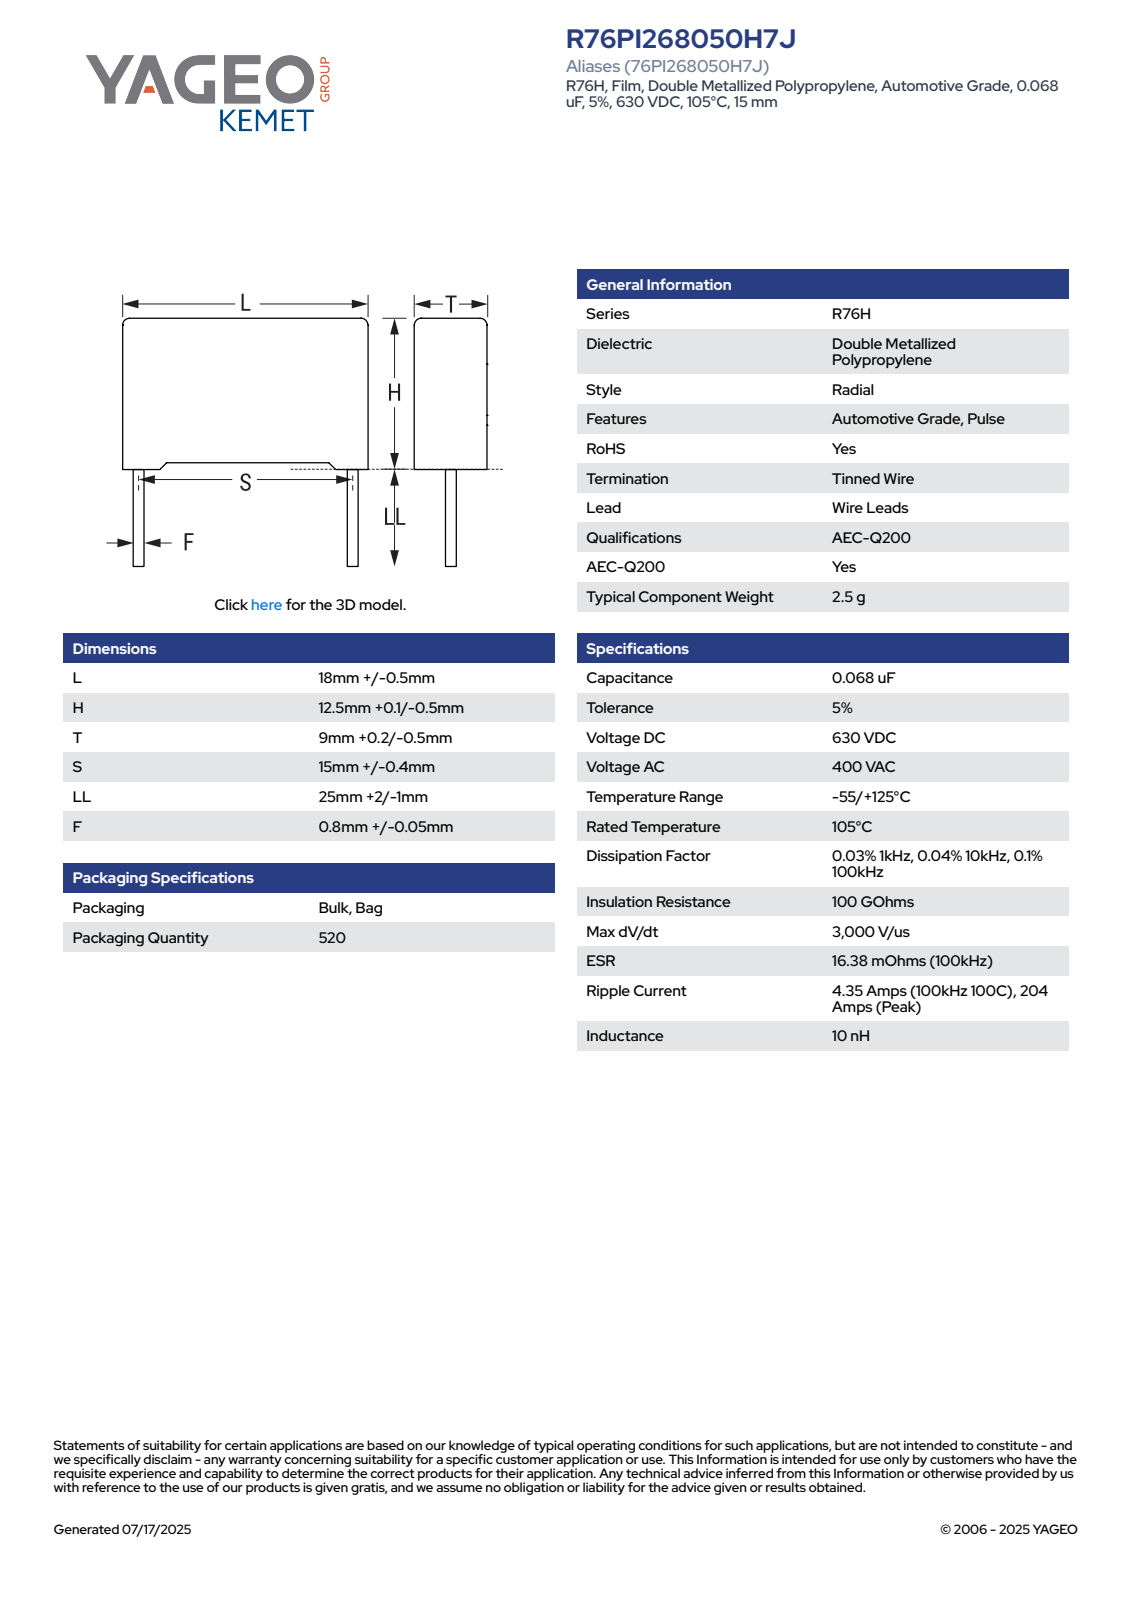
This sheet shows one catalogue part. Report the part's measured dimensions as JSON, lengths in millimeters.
{"part_name": "CFR_RB2R76_18X12.5X9_L18.5H12.6T9.2S15LL27F0.85", "step_written_by": "SolidWorks 2014 (AUTOMOTIVE_DESIGN)", "units": "millimeters", "bodies": {"solids": 4, "faces": 85, "planar": 77, "cylindrical": 8, "other": 0}, "overall_size": [39.6, 18.5, 9.21], "volume_mm3": 2064, "surface_area_mm2": 1219, "round_bosses_or_shafts": [[0.85, 2]], "partial_cylinders_radius": [[0.5, 4]], "face_to_face_distances": [9.2, 11.85, 18.5, 0.62, 0.75, 12.6, 8.58, 0.43, 0.32, 12.17]}
